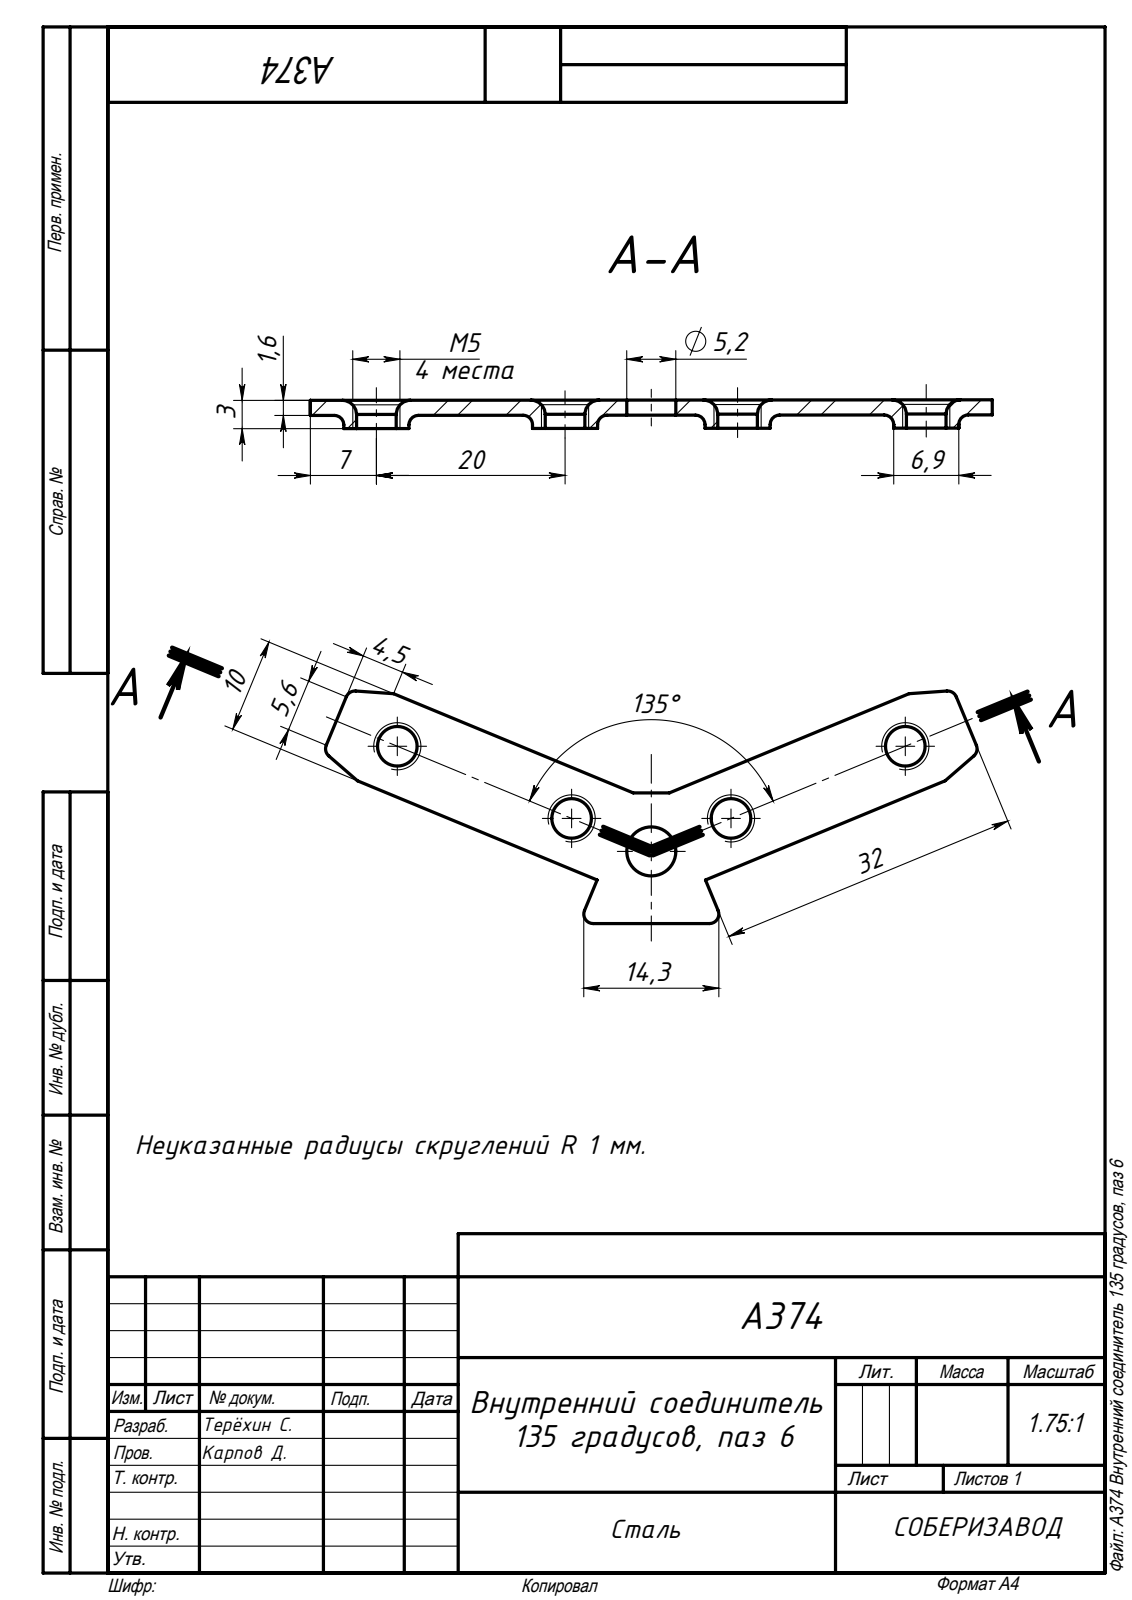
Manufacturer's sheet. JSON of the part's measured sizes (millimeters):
{"part_name": "A374 Внутренний соединитель 135 градусов, паз 6", "step_written_by": "SolidWorks 2020 (AUTOMOTIVE_DESIGN)", "units": "millimeters", "bodies": {"solids": 1, "faces": 62, "planar": 20, "cylindrical": 26, "other": 16}, "overall_size": [69.06, 24.67, 3], "volume_mm3": 1212, "surface_area_mm2": 1873, "round_holes": [[4.2, 4], [5.2, 1]], "round_bosses_or_shafts": [[6.9, 4]], "partial_cylinders_radius": [[1, 6]], "face_to_face_distances": [1.6, 1.4, 3, 10, 10.01, 32.01, 13.86], "hole_center_spacings": [9.15, 20, 29.15, 36.2, 16.9, 53.86]}
